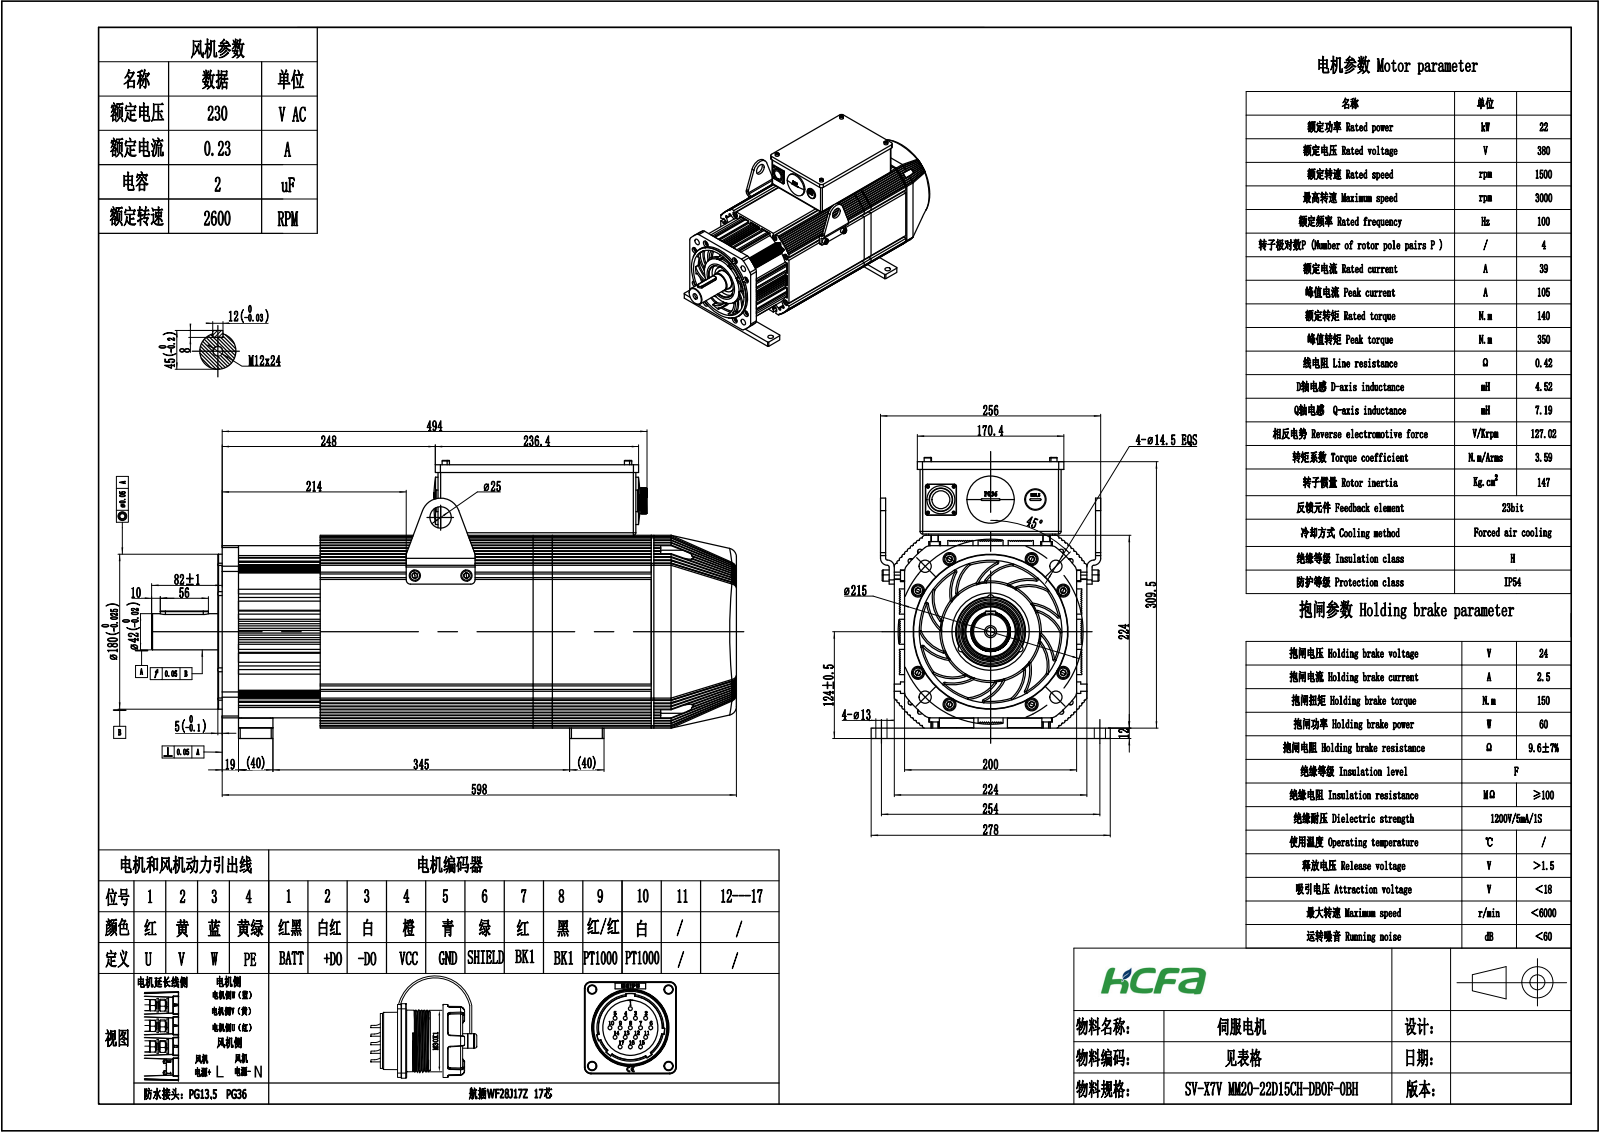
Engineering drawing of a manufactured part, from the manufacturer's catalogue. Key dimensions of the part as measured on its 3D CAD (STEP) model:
Part name (STEP PRODUCT): 10002030101-0038-SV-X7VMM20-22D15CH-DB0F-0BH-6段外形图
STEP written by: SolidWorks 2021 (CONFIG_CONTROL_DESIGN)
Units: millimetres
Bodies: 8 solids, 3820 faces (1620 planar, 1208 cylindrical, 992 other)
Overall size (bounding box): 679.9 × 326.5 × 278
Volume: 26 450 000 mm³ · Surface area: 1 173 000 mm²
Round holes (diameter × count): ⌀9 ×24, ⌀15 ×14, ⌀13 ×8, ⌀10 ×6, ⌀2.5 ×4, ⌀3.2 ×4, ⌀5.8 ×4, ⌀6.8 ×4, ⌀7 ×4, ⌀14.5 ×4, ⌀10.2 ×1, ⌀17 ×1
Round bosses / shafts (diameter × count): ⌀1.5 ×17, ⌀13 ×10, ⌀8 ×10, ⌀8.5 ×4, ⌀6.3 ×4, ⌀5 ×4, ⌀40 ×2, ⌀180 ×1
Partial cylindrical surfaces — rounded edges, fillets, slot ends (radius × count): R2 ×112, R1 ×24, R1.5 ×20, R5 ×18, R1.4 ×16, R3 ×12, R0.2 ×10, R10 ×10
Main face-to-face distances: 224, 307.5, 2, 12, 6, 309.5, 194, 85.5, 30, 212
Hole centre spacings: 29.47, 43.17, 97, 124.07, 137.18, 138.41, 162.9, 167.15
